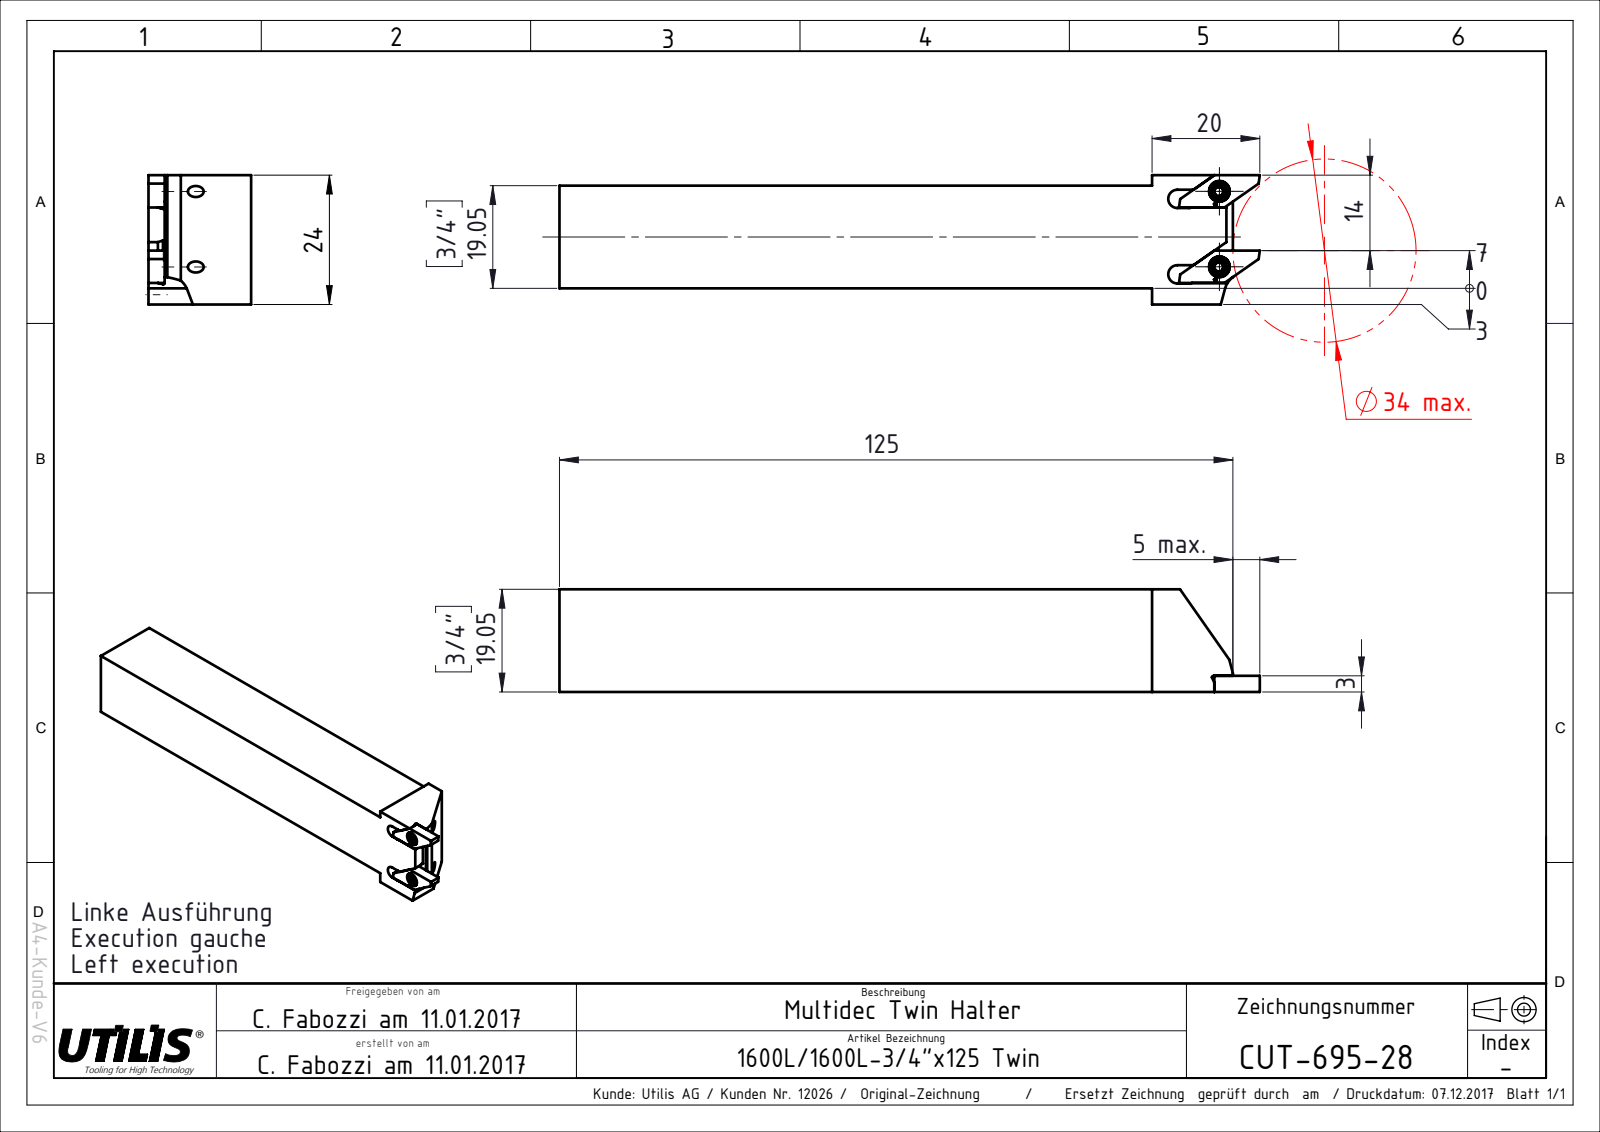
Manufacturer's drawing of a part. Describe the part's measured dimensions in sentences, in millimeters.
The part is named "CUT-695-28". Its 3-D file was written by "SolidWorks 2016 (AUTOMOTIVE_DESIGN)". It is 1 solid with 86 faces: 77 planar, 9 cylindrical and 0 other. Overall it measures 130 by 24 by 19.05 millimeters. Its volume is 45 029 cubic millimeters and its surface area 10 482 square millimeters. Partial cylindrical surfaces (rounded edges, fillets, slot ends): 2 of radius 0.5, 2 of radius 1.55, 2 of radius 1.7, 1 of radius 4.1. The main face-to-face distances are 19.05, 1.95, 21, 3, 22.05, 24, 110, 16.05, 14, 6.
